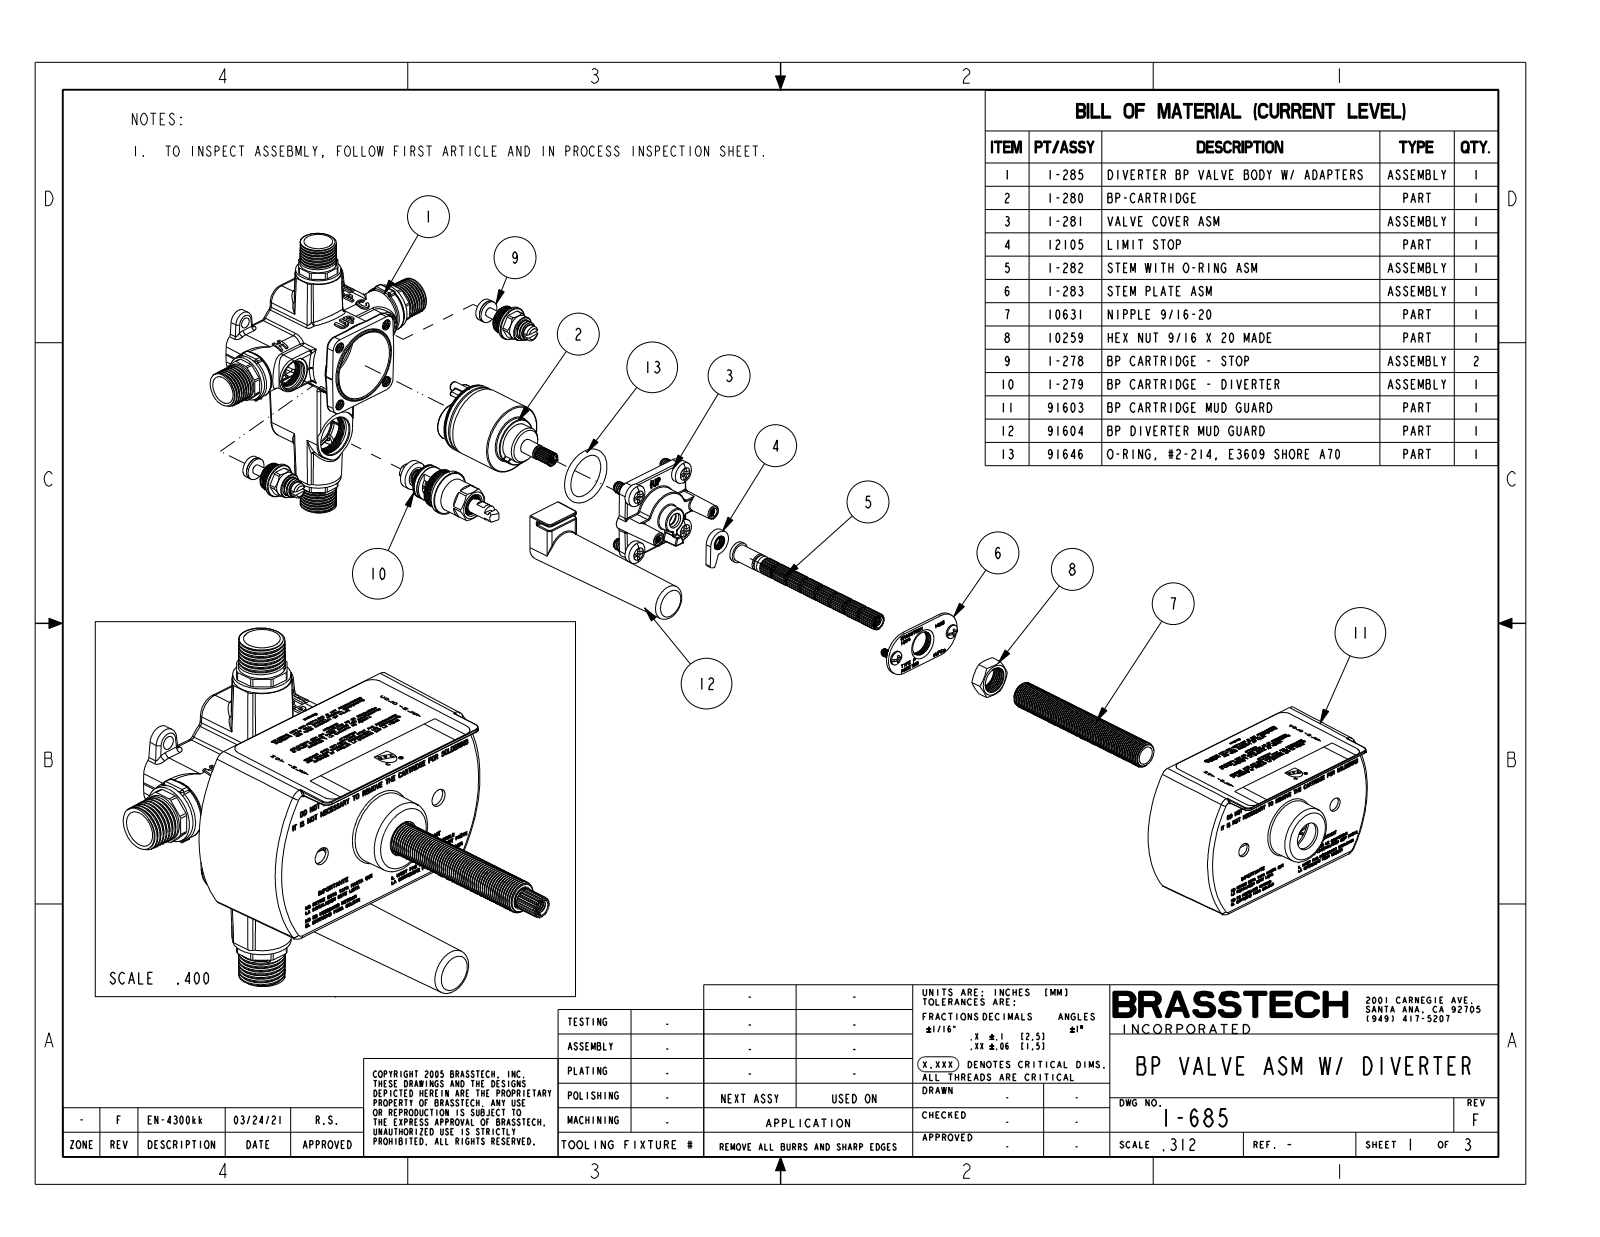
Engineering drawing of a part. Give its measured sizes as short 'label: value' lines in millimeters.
name: 12103; 12136; 1-285_ASM; 1-280 (+8 more)
written by: CREO PARAMETRIC BY PTC INC, 2018400 (AUTOMOTIVE_DESIGN)
unit: mm
bodies: 35 solids, 11783 faces (8669 planar, 1504 cylindrical, 1610 other)
size: 198.8 × 170 × 150.8
volume: 432 100 mm³; area: 181 900 mm²
holes: 4× ⌀6.6, 3× ⌀3.3, 2× ⌀5.1, 2× ⌀5.5, 2× ⌀8, 2× ⌀9.2, 2× ⌀11.5, 2× ⌀14.8, 2× ⌀16, 1× ⌀1.4, 1× ⌀1.8, 1× ⌀2.5
bosses: 5× ⌀4.7, 4× ⌀12.5, 4× ⌀8, 4× ⌀6.3, 3× ⌀19, 3× ⌀5.2, 3× ⌀4.8, 2× ⌀25.4
rounds: 62× R0.5, 20× R0.1, 16× R2, 12× R0.3, 10× R0.8, 6× R2.5, 6× R8, 4× R1.5
face distances: 1.5, 37.5, 36, 30.5, 6.3, 5.5, 32, 1.6, 12.5, 5
hole spacings: 18.6, 25.5, 26, 36.8, 43.9, 57.4, 14.5, 18.6
